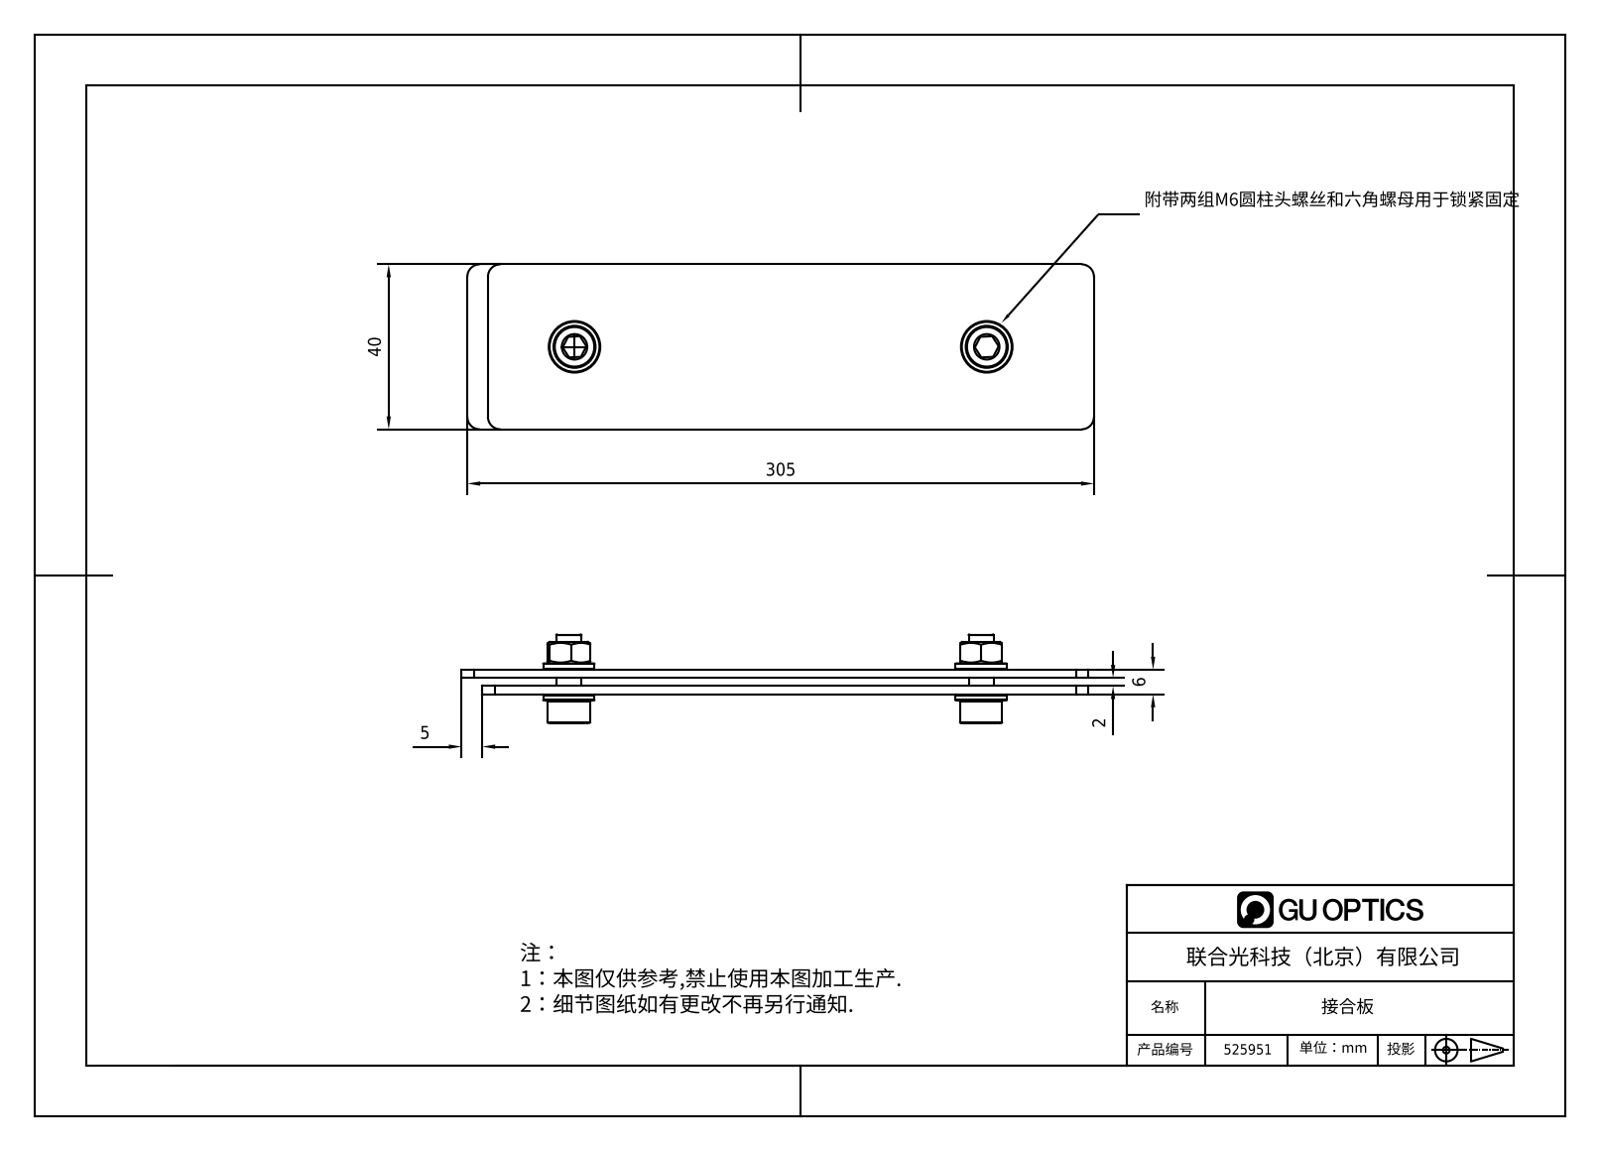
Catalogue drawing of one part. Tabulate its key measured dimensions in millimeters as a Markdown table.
| quantity | value |
| --- | --- |
| part name | 525951 |
| STEP written by | SolidWorks 2020 (CONFIG_CONTROL_DESIGN) |
| units | millimeters |
| bodies | 10 solids, 114 faces (56 planar, 26 cylindrical, 32 other) |
| overall size | 305 × 40 × 21.5 |
| volume | 51 005 mm³ |
| surface area | 54 101 mm² |
| round holes (diameter × count) | 6.4 × 2, 6.6 × 2, 4.92 × 1, 4.92 × 1 |
| round bosses / shafts (diameter × count) | 12.5 × 2, 10.2 × 2, 6 × 2 |
| partial cylindrical surfaces (radius × count) | 3 × 6 |
| main face-to-face distances | 2, 4, 6, 40, 5.5, 1.5, 3.5, 7.5, 9, 10 |
| hole center spacings | 200 |
